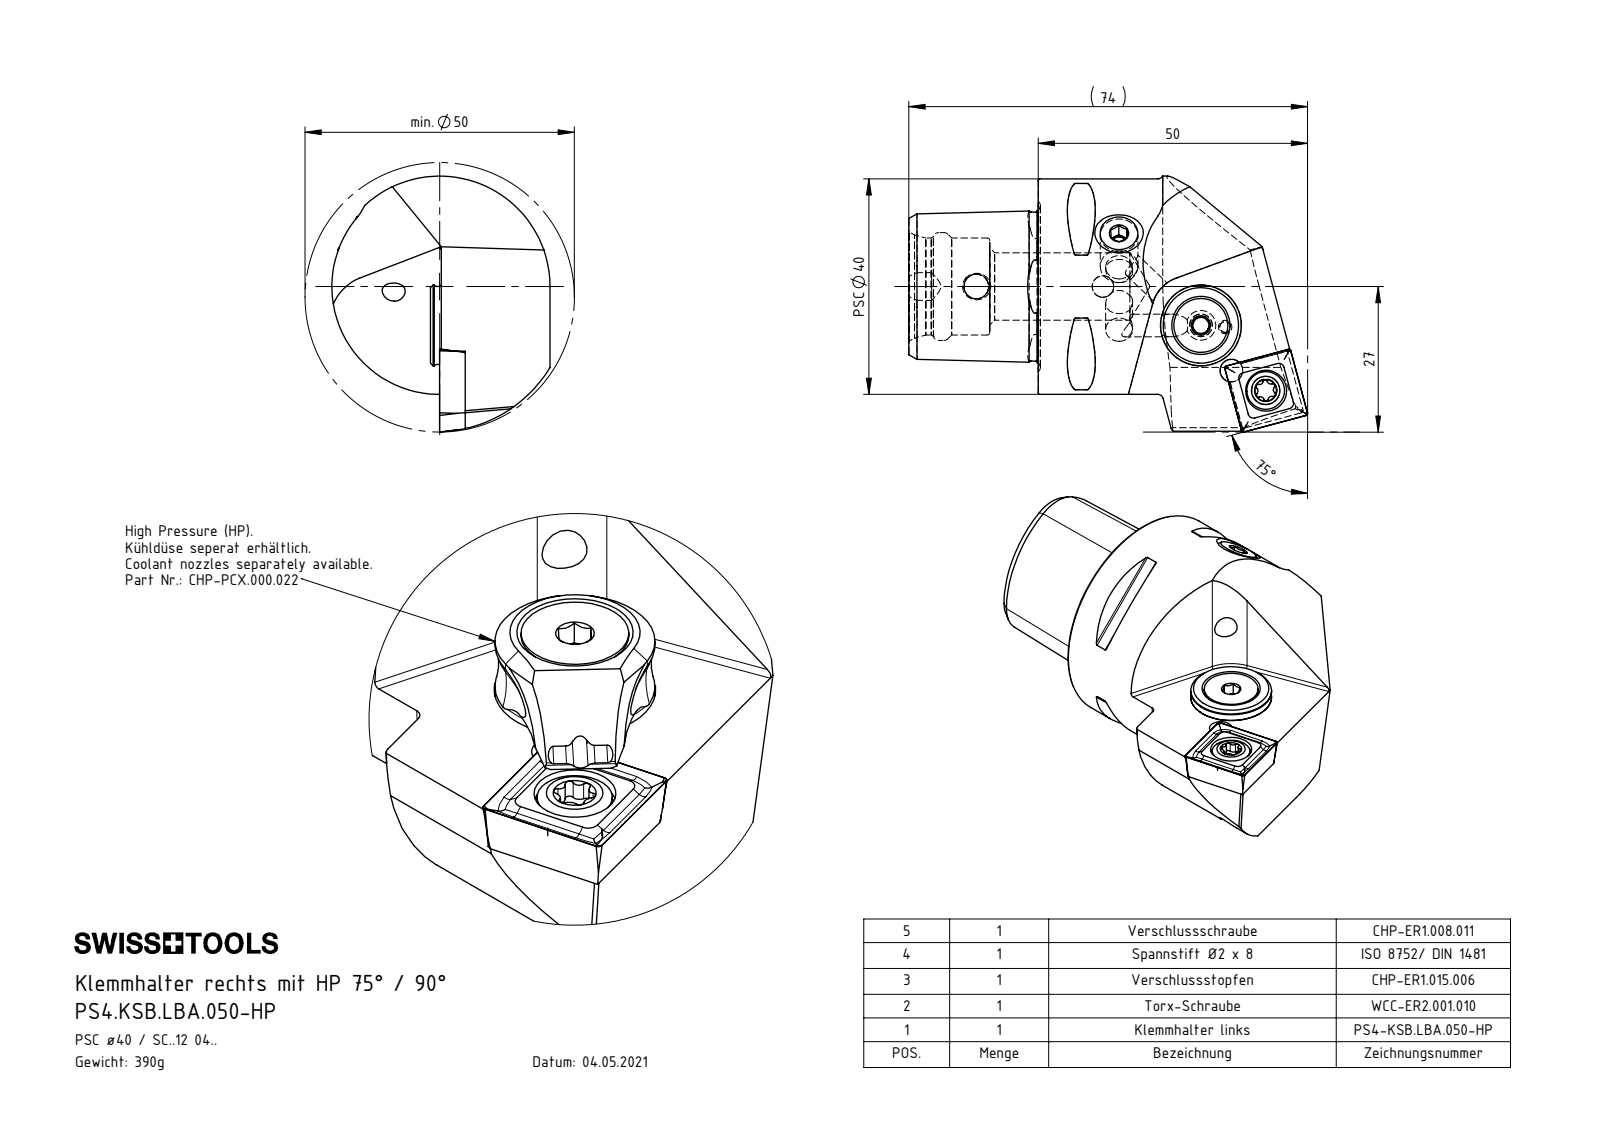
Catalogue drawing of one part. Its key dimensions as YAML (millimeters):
part_name: "PS4.KSB.LBA.050-HP; WCC-ER2.001.010_A; SCMT120404; DIN 3771 - 6.5x1.5 (+7 more)"
step_written_by: "SolidWorks 2022 (CONFIG_CONTROL_DESIGN)"
units: millimeters
bodies: {solids: 9, faces: 483, planar: 101, cylindrical: 133, other: 249}
overall_size: [74, 47.5, 40.5]
volume: 50533
surface_area: 16417
round_holes:
  - {diameter: 4.2, count: 5}
  - {diameter: 1.2, count: 1}
  - {diameter: 2, count: 1}
  - {diameter: 3, count: 1}
  - {diameter: 4, count: 1}
  - {diameter: 4.6, count: 1}
  - {diameter: 5, count: 1}
  - {diameter: 5.3, count: 1}
  - {diameter: 5.5, count: 1}
  - {diameter: 7, count: 1}
  - {diameter: 7.6, count: 1}
  - {diameter: 12.5, count: 1}
round_bosses_or_shafts:
  - {diameter: 5, count: 2}
  - {diameter: 40, count: 1}
  - {diameter: 14.85, count: 1}
  - {diameter: 13.4, count: 1}
  - {diameter: 10, count: 1}
  - {diameter: 8, count: 1}
  - {diameter: 7, count: 1}
  - {diameter: 5.5, count: 1}
partial_cylinders:
  - {radius: 0.3, count: 9}
  - {radius: 1, count: 7}
  - {radius: 0.39, count: 6}
  - {radius: 0.69, count: 6}
  - {radius: 0.5, count: 4}
  - {radius: 6, count: 3}
  - {radius: 1.1, count: 2}
  - {radius: 1.2, count: 2}
face_to_face_distances: [20.2, 15.74, 4.46, 24, 15.7, 4.5, 15.52, 1.5, 3, 17.2]
hole_center_spacings: [4.5, 7.35, 7.45, 8.15, 10.11, 13.96, 14.05, 17.03]
